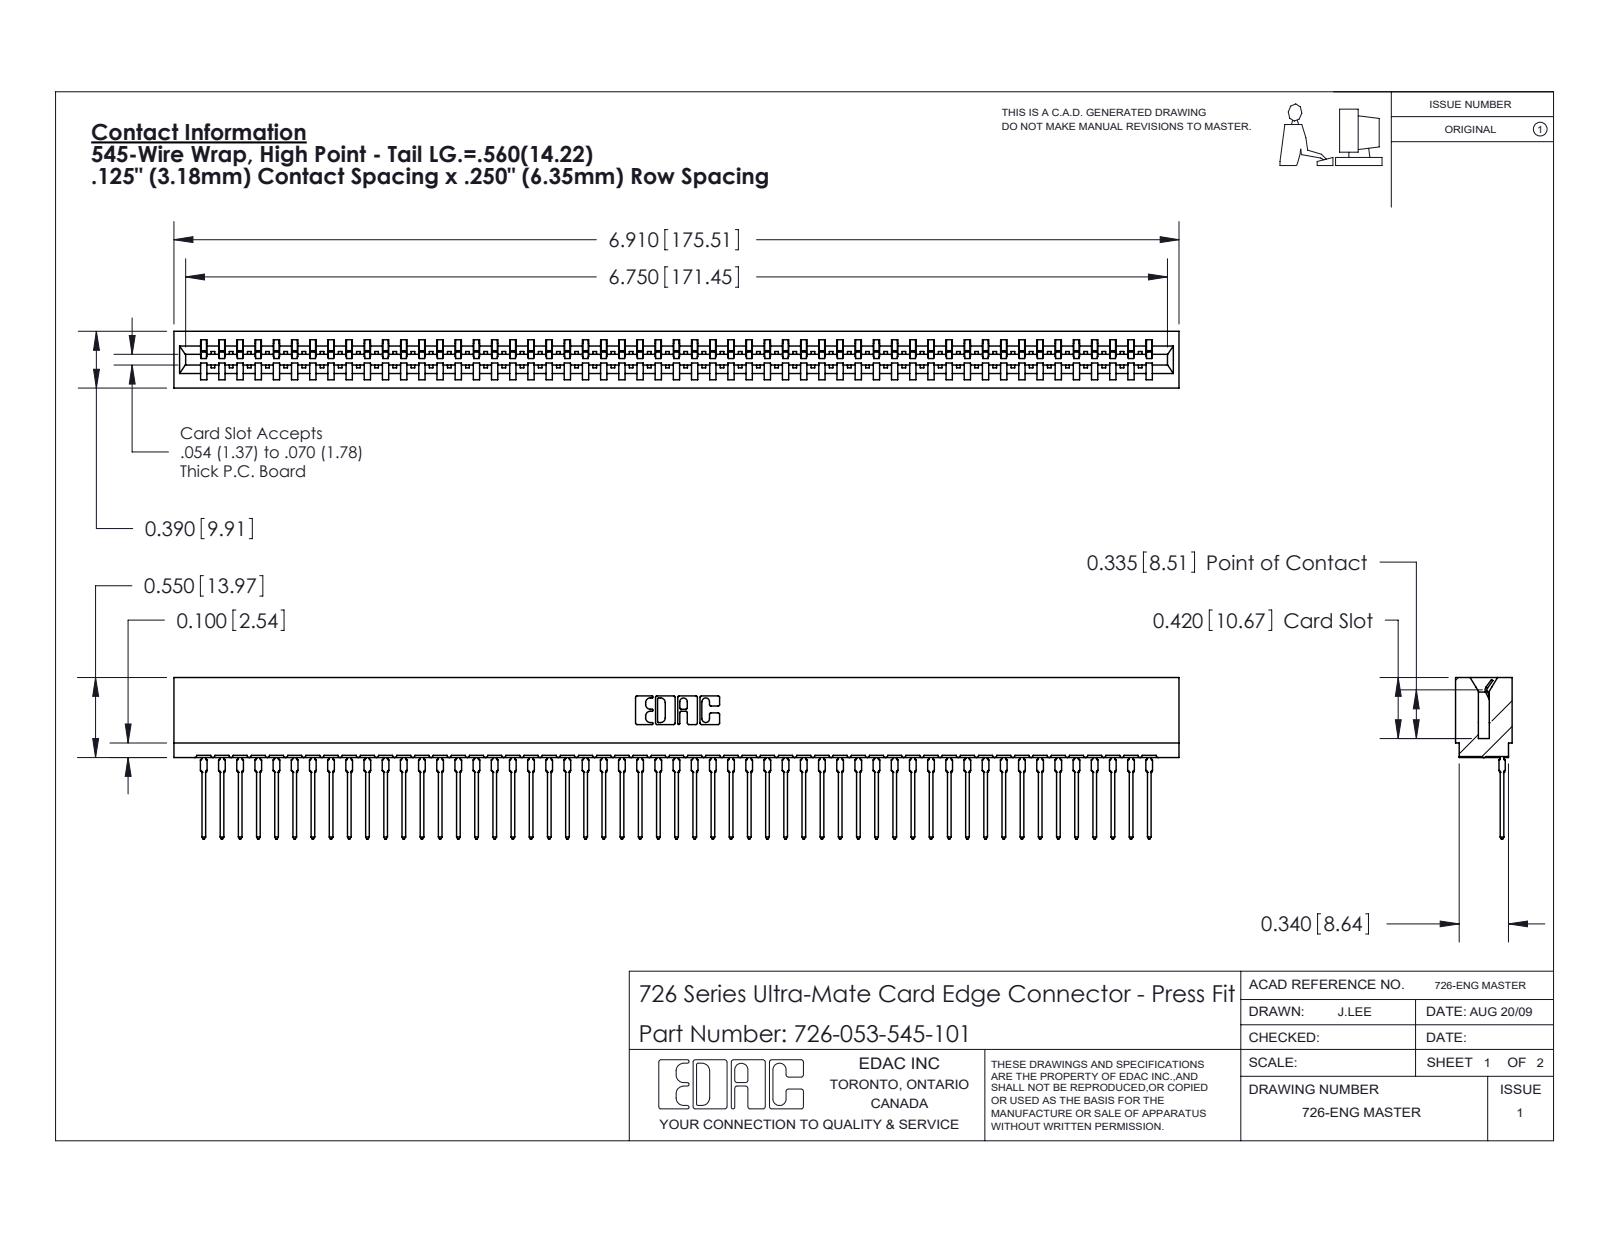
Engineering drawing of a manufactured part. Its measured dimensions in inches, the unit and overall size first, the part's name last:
Units: inches
Overall size (bounding box): 6.91 × 1.109 × 0.39
Partial cylindrical surfaces — rounded edges, fillets, slot ends (radius × count): R0.021 ×106, R0.015 ×54, R0.01 ×22, R0.007 ×6, R0.031 ×6, R0.005 ×4, R0.011 ×4, R0.026 ×3
Main face-to-face distances: 0.057, 0.333, 0.39, 0.025, 0.307, 0.25, 0.083, 0.275, 0.365, 0.032
Volume: 0.961 in³ · Surface area: 38.67 in²
Bodies: 54 solids, 5821 faces (3394 planar, 1049 cylindrical, 1378 other)
Part name (STEP PRODUCT): 726 Part_.515 Slot Depth - 01; 726-053-545-101; 746-292-001_545
STEP written by: SolidWorks 2020 (CONFIG_CONTROL_DESIGN)
